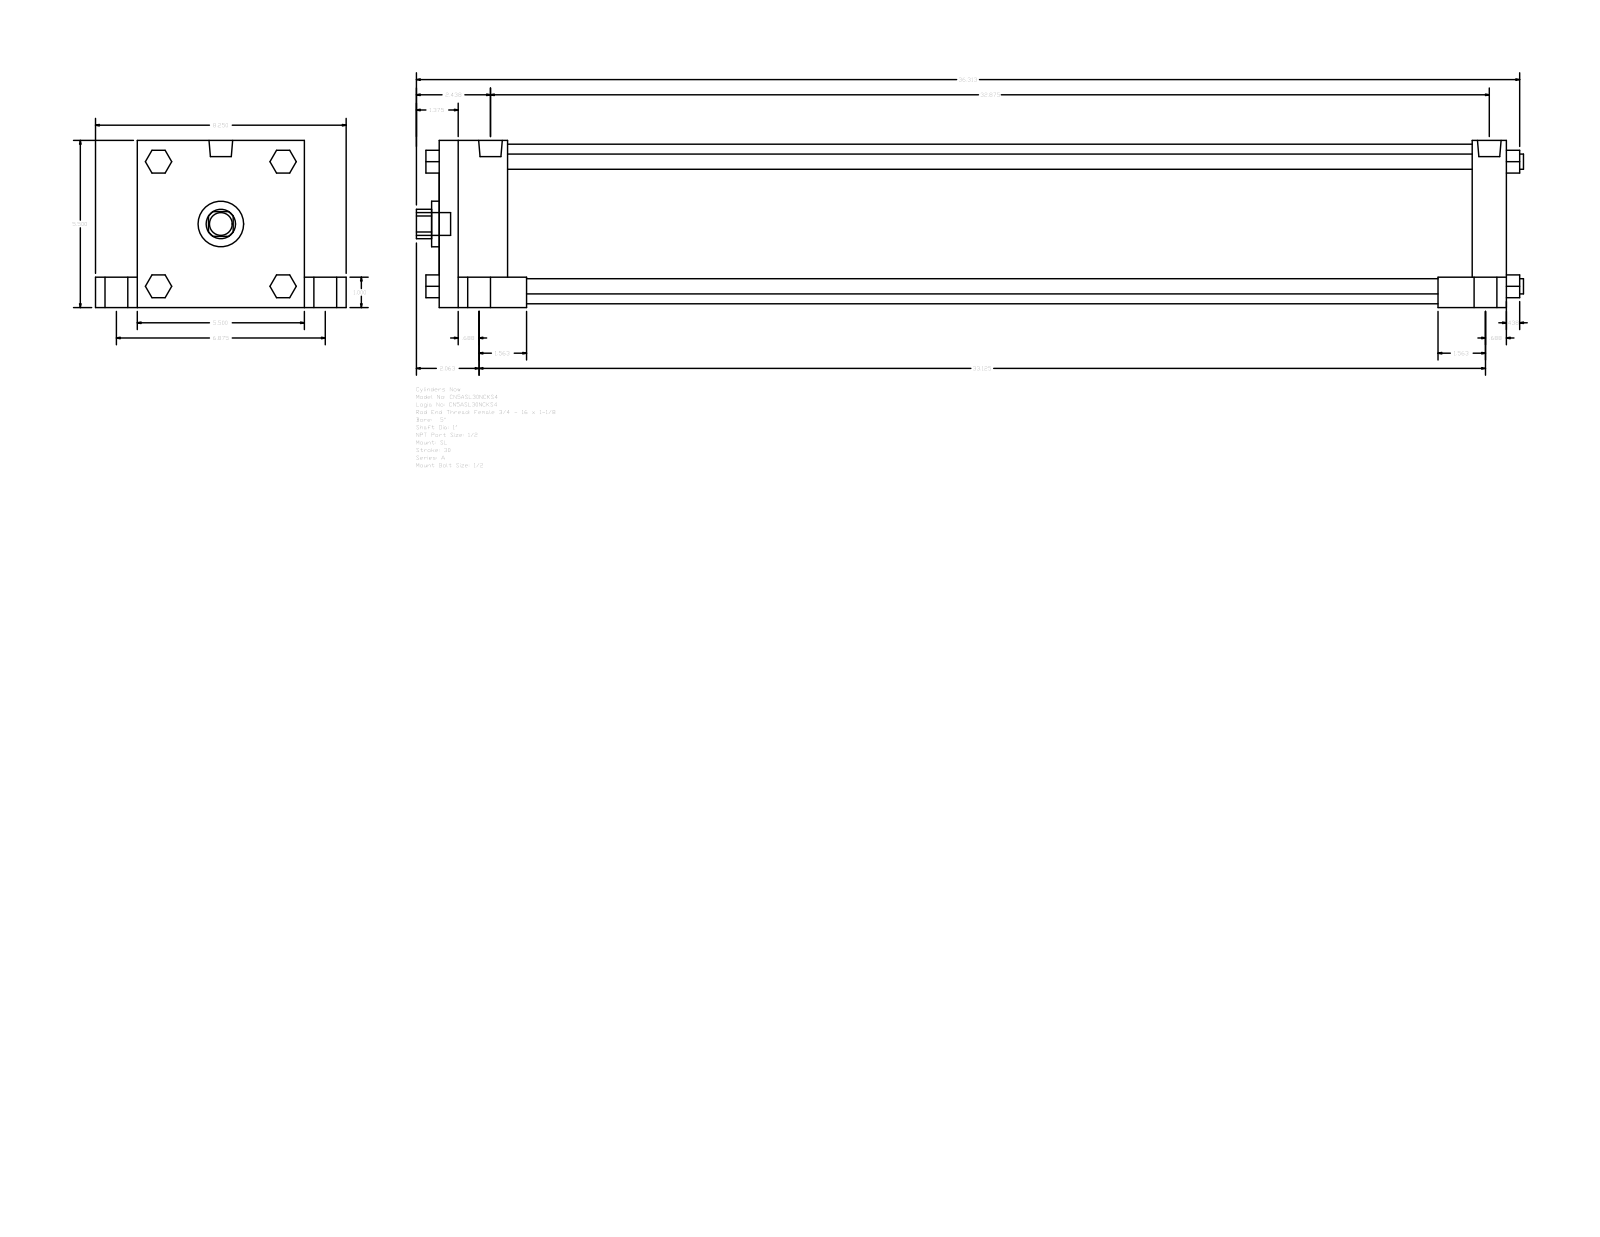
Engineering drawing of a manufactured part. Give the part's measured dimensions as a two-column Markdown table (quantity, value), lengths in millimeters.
| quantity | value |
| --- | --- |
| part name | A_SL__0500_1 |
| STEP written by | GSSL Pune (CONFIG_CONTROL_DESIGN) |
| units | millimeters |
| bodies | 0 solids, 150 faces (114 planar, 36 cylindrical, 0 other) |
| overall size | 925.51 × 209.55 × 139.7 |
| round holes (diameter × count) | 25.4 × 1, 38.1 × 1, 133.35 × 1 |
| round bosses / shafts (diameter × count) | 19.05 × 5, 25.4 × 4, 12.7 × 4, 8.73 × 4, 19.77 × 2 |
| partial cylindrical surfaces (radius × count) | 12.29 × 1 |
| main face-to-face distances | 139.7, 892.18, 57.15, 835.03, 25.4, 114.3, 34.93, 174.63, 863.6, 806.45 |
